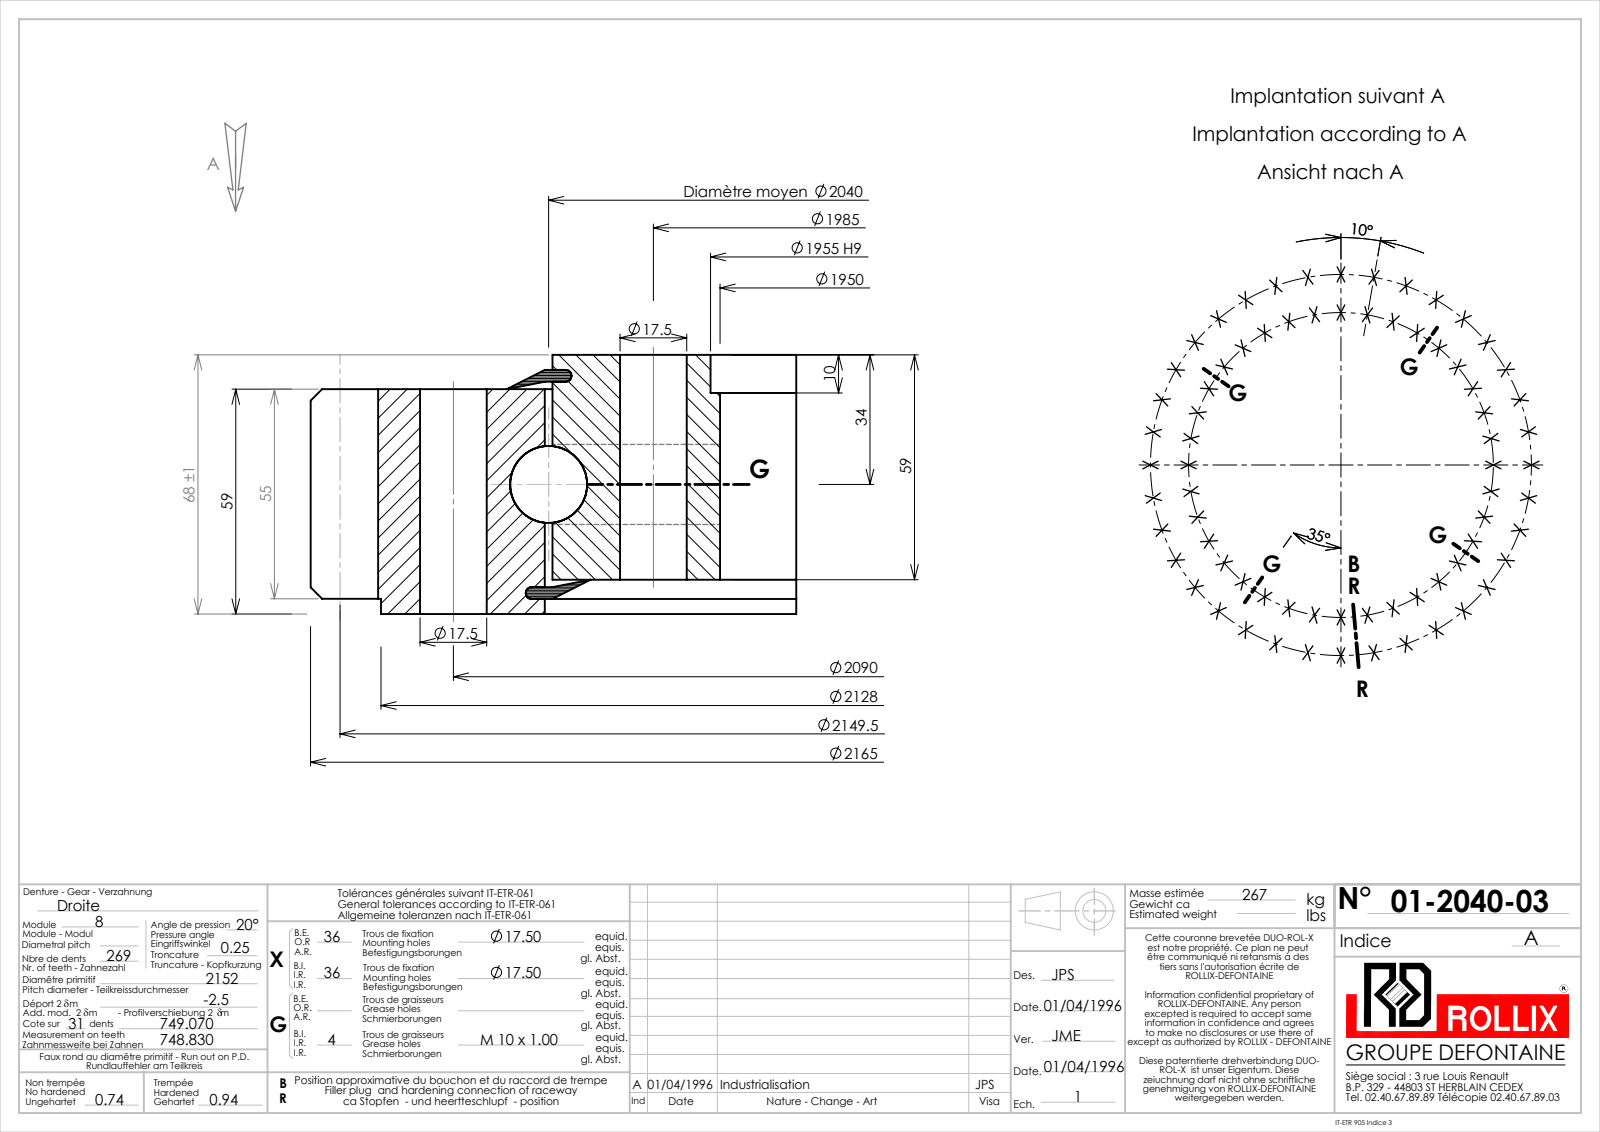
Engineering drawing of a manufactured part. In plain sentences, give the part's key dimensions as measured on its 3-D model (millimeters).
The part is named "01-2040-03". Its 3-D file was written by "SolidWorks 2016 (CONFIG_CONTROL_DESIGN)". It is 5 solids with 1828 faces: 552 planar, 709 cylindrical and 567 other. Overall it measures 2165 by 2164.97 by 68 millimeters. Its volume is 33 930 000 cubic millimeters and its surface area 4 041 000 square millimeters. Round holes: 72 of diameter 17.5, 4 of diameter 9, 1 of diameter 1950, 1 of diameter 1955, 1 of diameter 2042.02, 1 of diameter 2042.03. Round bosses or shafts: 1 of diameter 2128, 1 of diameter 2037.97. Partial cylindrical surfaces (rounded edges, fillets, slot ends): 1 of radius 1064.75, 1 of radius 1082.5. The main face-to-face distances are 59, 9, 50, 68, 7.05, 60.95, 1.95, 51.95, 3.95, 64.05. The hole center spacings are 1045, 362.92, 1712.03, 2058.25, 1963.96, 540.93, 1477.85, 1894.18.
